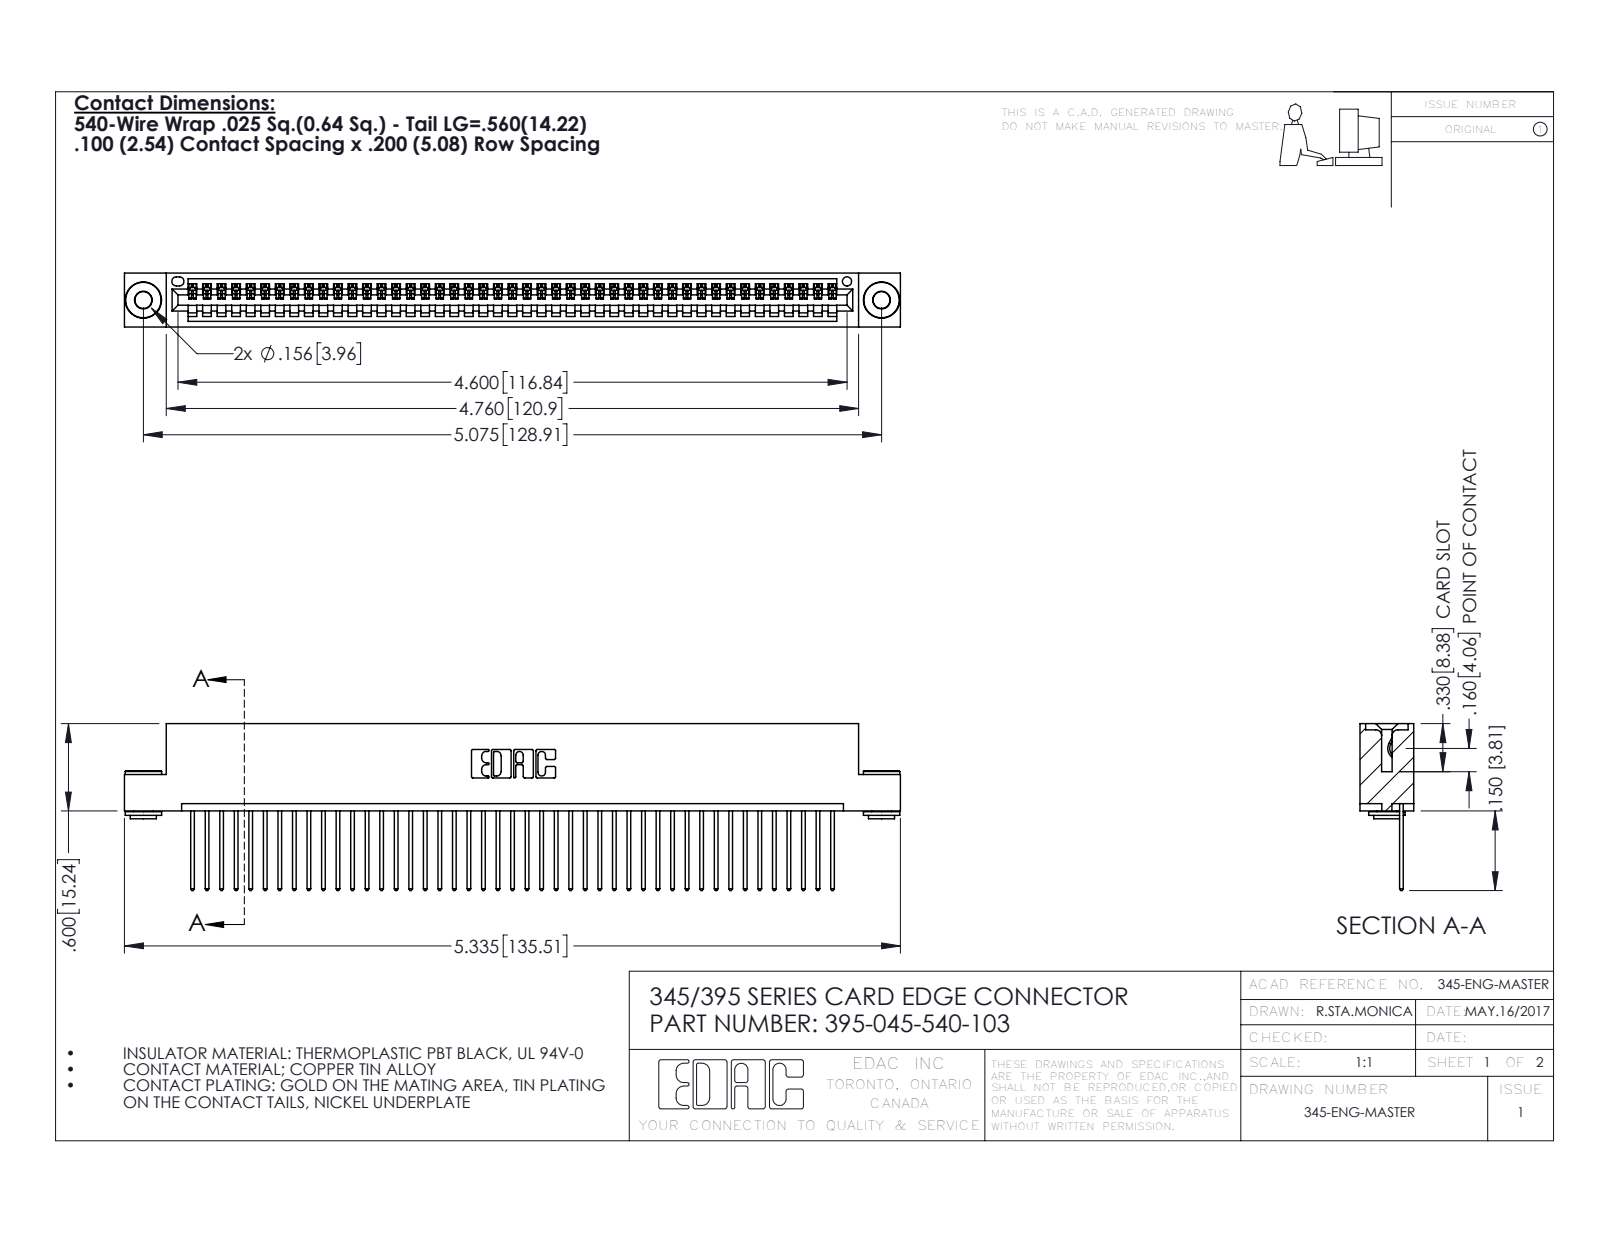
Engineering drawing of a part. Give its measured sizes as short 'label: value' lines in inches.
name: 345-250-002_345-250-002-102; 345-292-001_345-293-140; 345 Part_Flush Mounting Lugs - 0.156 Dia-TH; 395-045-540-103
written by: SolidWorks 2016 (CONFIG_CONTROL_DESIGN)
unit: in
bodies: 48 solids, 2774 faces (1890 planar, 876 cylindrical, 8 other)
size: 5.335 × 1.147 × 0.37
volume: 0.792 in³; area: 27.8 in²
holes: 2× ⌀0.116, 2× ⌀0.156, 1× ⌀0.064
bosses: 2× ⌀0.25, 2× ⌀0.18, 2× ⌀0.136
rounds: 90× R0.006, 90× R0.01, 22× R0.01, 6× R0.007, 6× R0.031, 3× R0.026, 2× R0.031, 2× R0.04
face distances: 0.072, 0.298, 0.37, 0.2, 0.025, 0.098, 0.272, 0.225, 0.149, 0.072
hole spacings: 0.27, 4.839, 5.075
